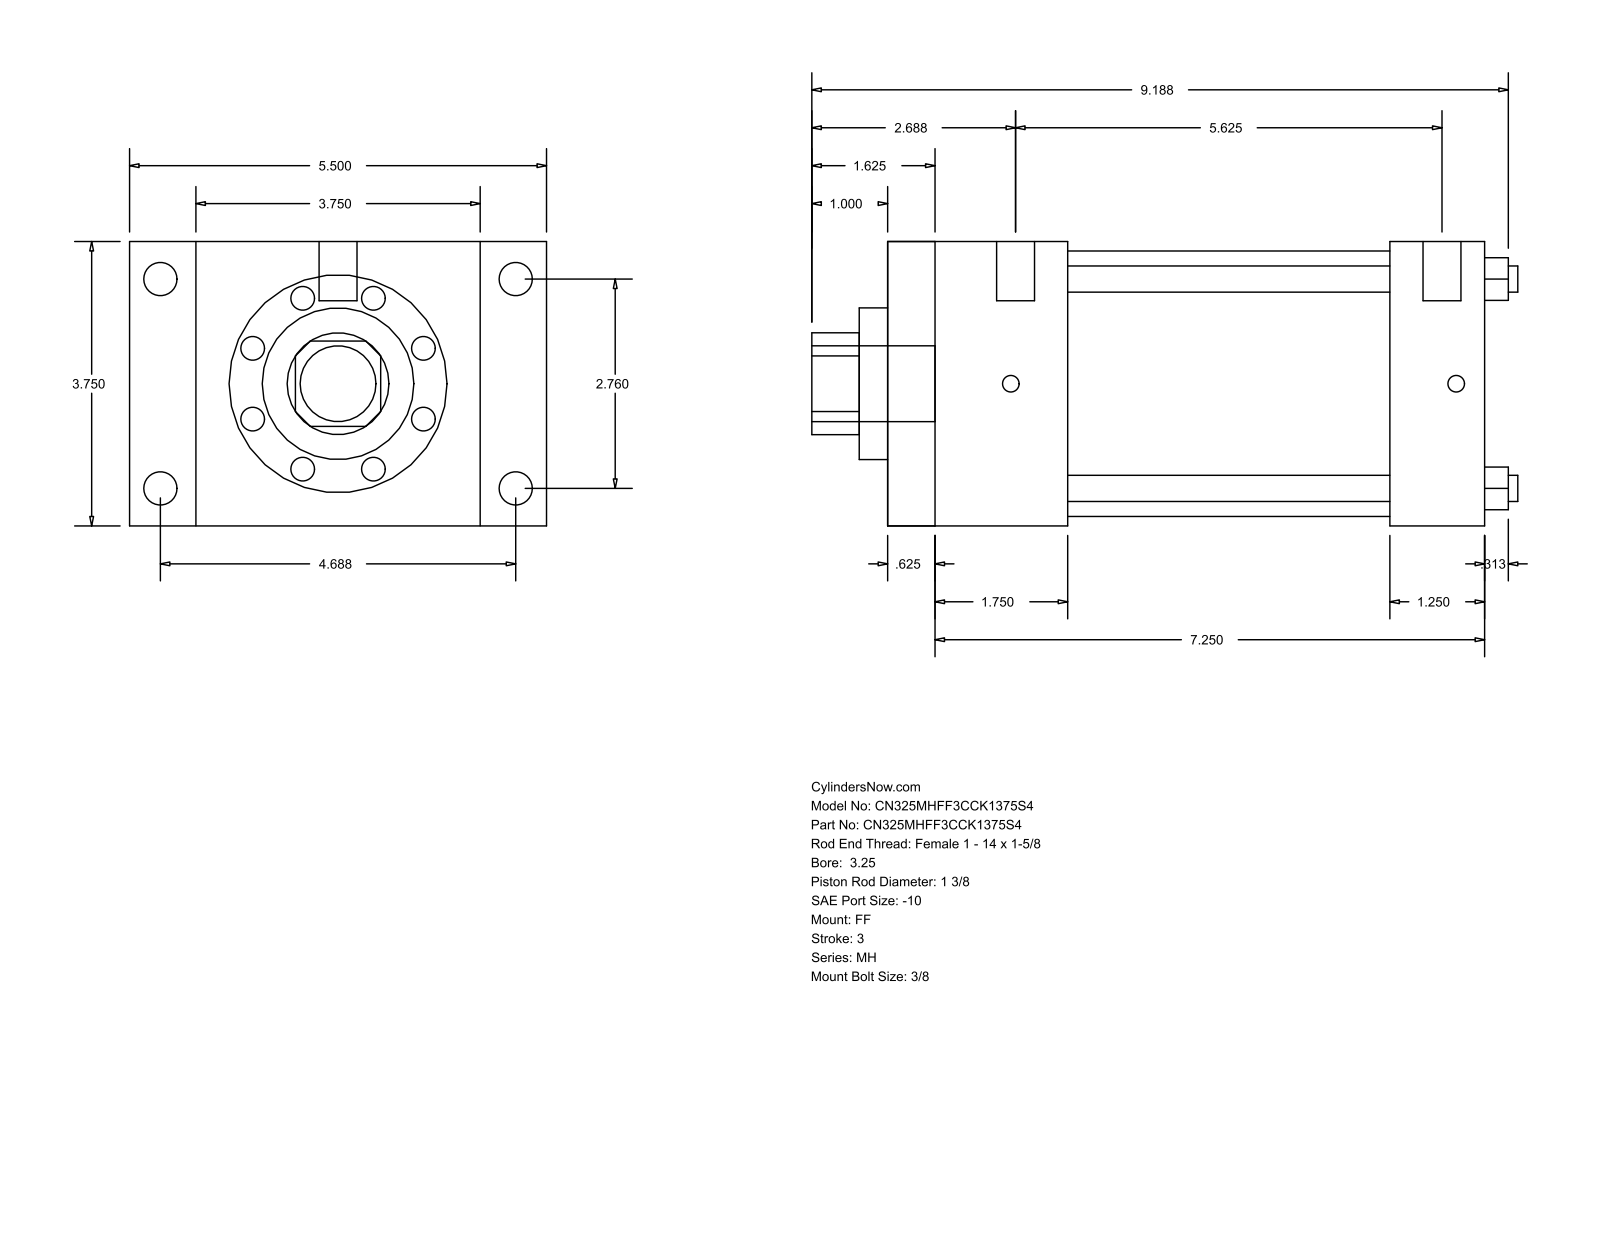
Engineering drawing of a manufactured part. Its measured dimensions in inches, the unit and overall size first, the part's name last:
Units: inches
Overall size (bounding box): 9.313 × 5.5 × 3.75
Round holes (diameter × count): ⌀0.345 ×4, ⌀1.375 ×1, ⌀2 ×1, ⌀3.5 ×1
Round bosses / shafts (diameter × count): ⌀0.438 ×4, ⌀0.219 ×4, ⌀0.5 ×2, ⌀1 ×1
Partial cylindrical surfaces — rounded edges, fillets, slot ends (radius × count): R0.672 ×1
Main face-to-face distances: 3.75, 7.875, 0.625, 7.25, 0.875, 4.625, 6.625, 6, 1.25, 2.375
Hole centre spacings: 1.952, 2.76, 3.903
Bodies: 0 solids, 92 faces (64 planar, 28 cylindrical, 0 other)
Part name (STEP PRODUCT): MH_FF__0325_1.375
STEP written by: GSSL Pune (CONFIG_CONTROL_DESIGN)
